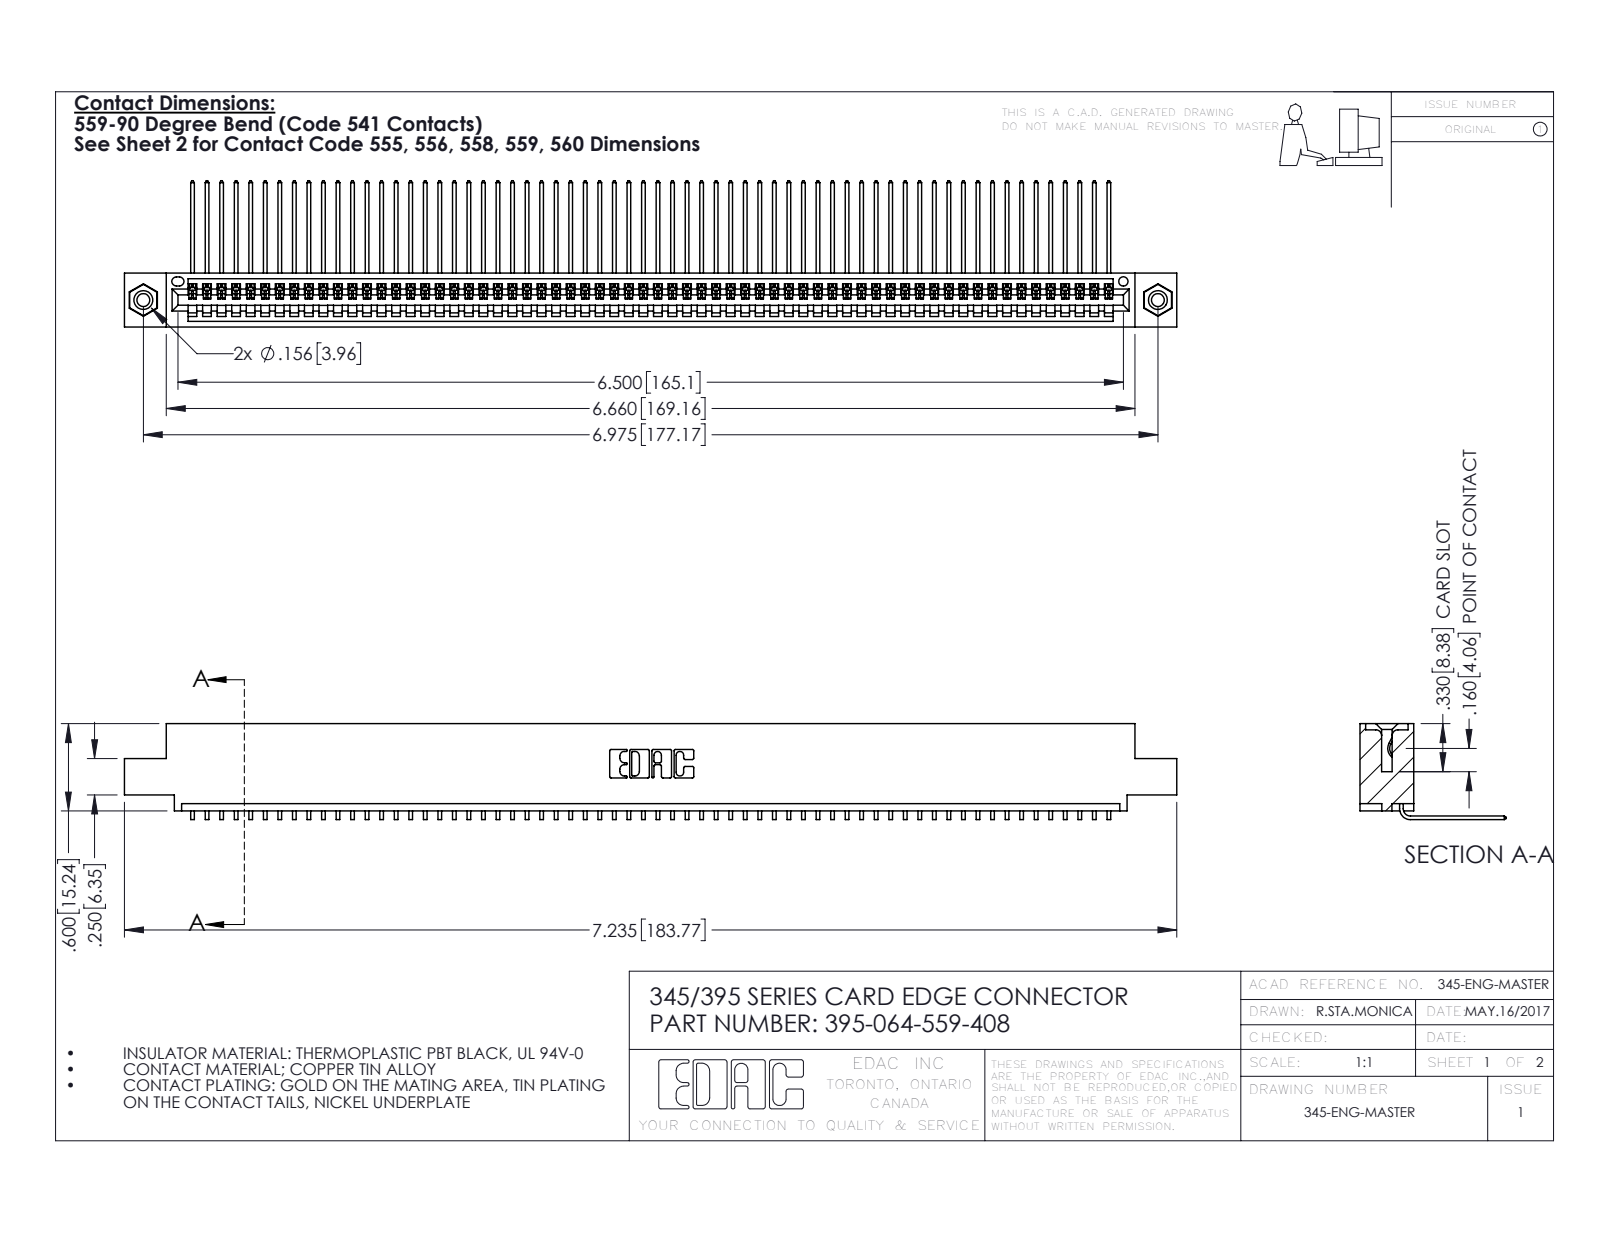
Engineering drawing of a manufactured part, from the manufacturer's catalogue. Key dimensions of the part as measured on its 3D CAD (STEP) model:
Part name (STEP PRODUCT): 345 Part_0.110 Offset - 0.156 Dia-TI; 345-250-001_345-250-003-102; 395-064-559-408; 345-292-001_558 559 Tail - 1
STEP written by: SolidWorks 2016 (CONFIG_CONTROL_DESIGN)
Units: inches
Bodies: 67 solids, 4030 faces (2804 planar, 1210 cylindrical, 16 other)
Overall size (bounding box): 7.235 × 1.005 × 0.659
Volume: 1.084 in³ · Surface area: 39.16 in²
Round holes (diameter × count): ⌀0.089 ×2, ⌀0.125 ×2, ⌀0.156 ×2, ⌀0.064 ×1
Round bosses / shafts (diameter × count): ⌀0.155 ×2
Partial cylindrical surfaces — rounded edges, fillets, slot ends (radius × count): R0.006 ×128, R0.01 ×22, R0.007 ×6, R0.031 ×6, R0.026 ×3, R0.031 ×2, R0.04 ×2, R0.014 ×1
Main face-to-face distances: 0.072, 0.298, 0.37, 0.2, 0.098, 0.272, 0.025, 0.225, 0.149, 0.072
Hole centre spacings: 0.27, 6.739, 6.975
